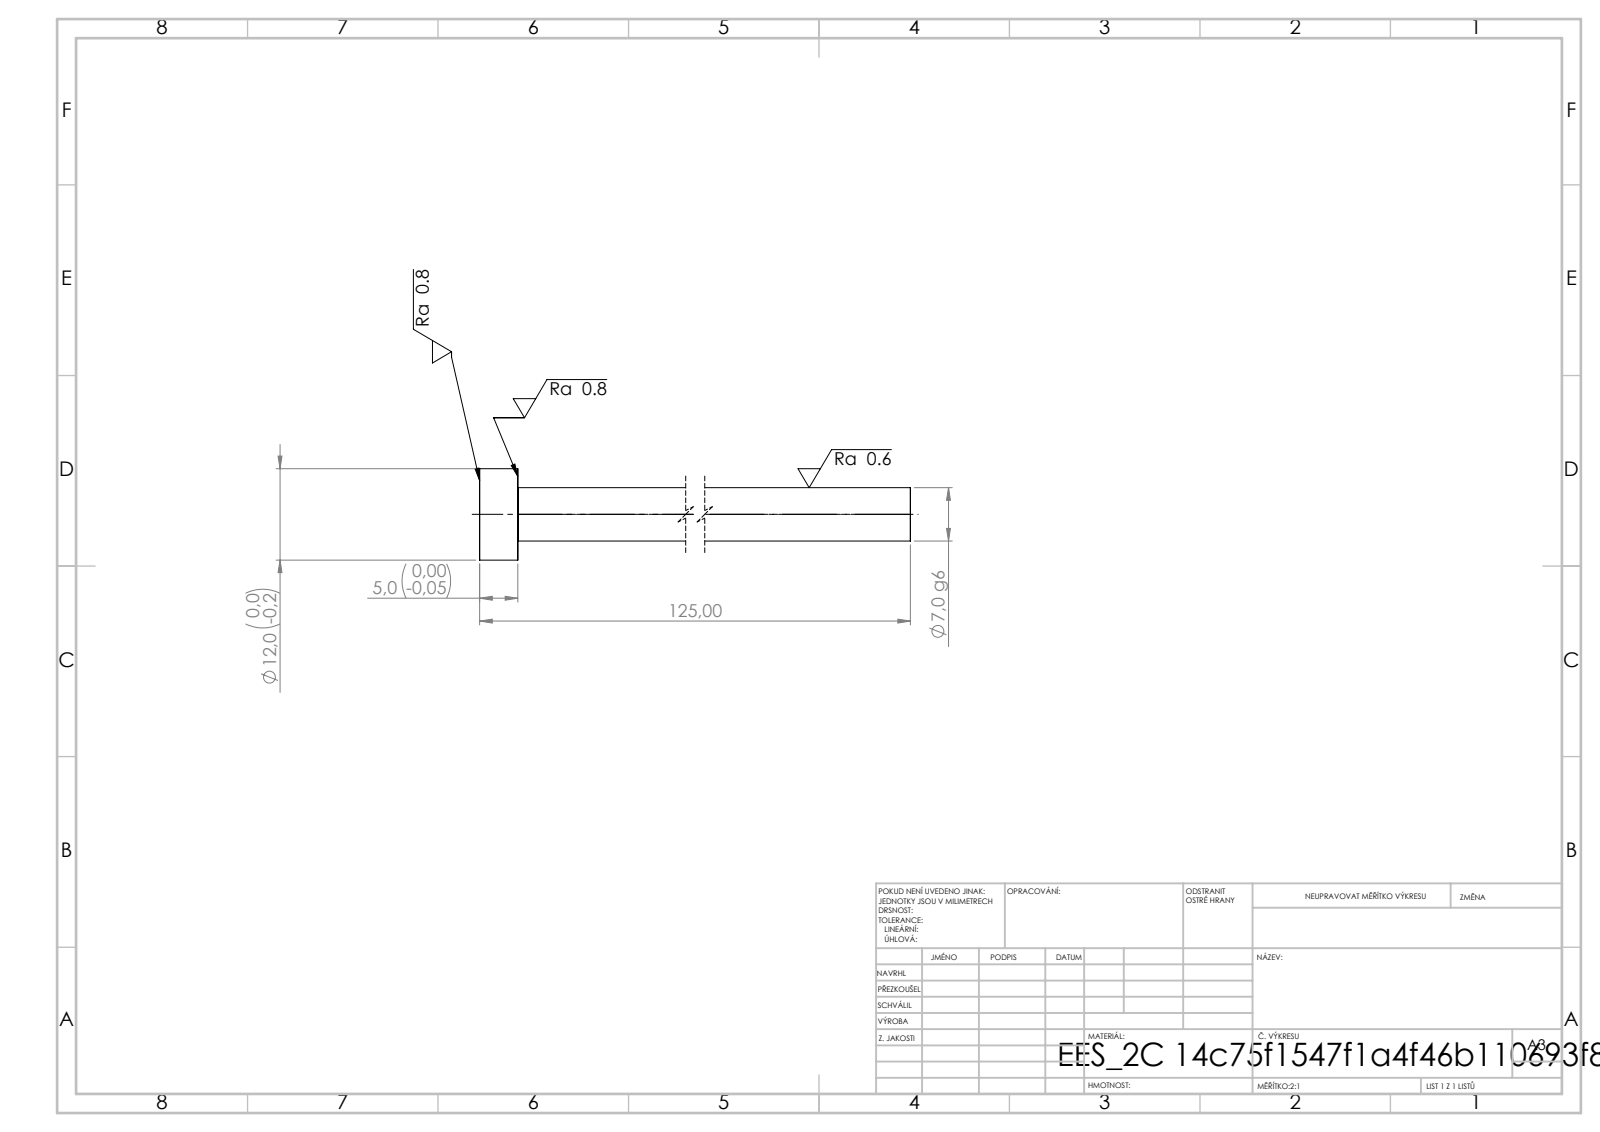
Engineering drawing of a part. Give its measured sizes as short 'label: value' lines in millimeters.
written by: SolidWorks 2019 (CONFIG_CONTROL_DESIGN)
unit: mm
bodies: 1 solid, 7 faces (3 planar, 4 cylindrical, 0 other)
size: 125 × 12 × 12
volume: 5 184 mm³; area: 3 054 mm²
bosses: 1× ⌀12, 1× ⌀7
face distances: 5, 125, 120
